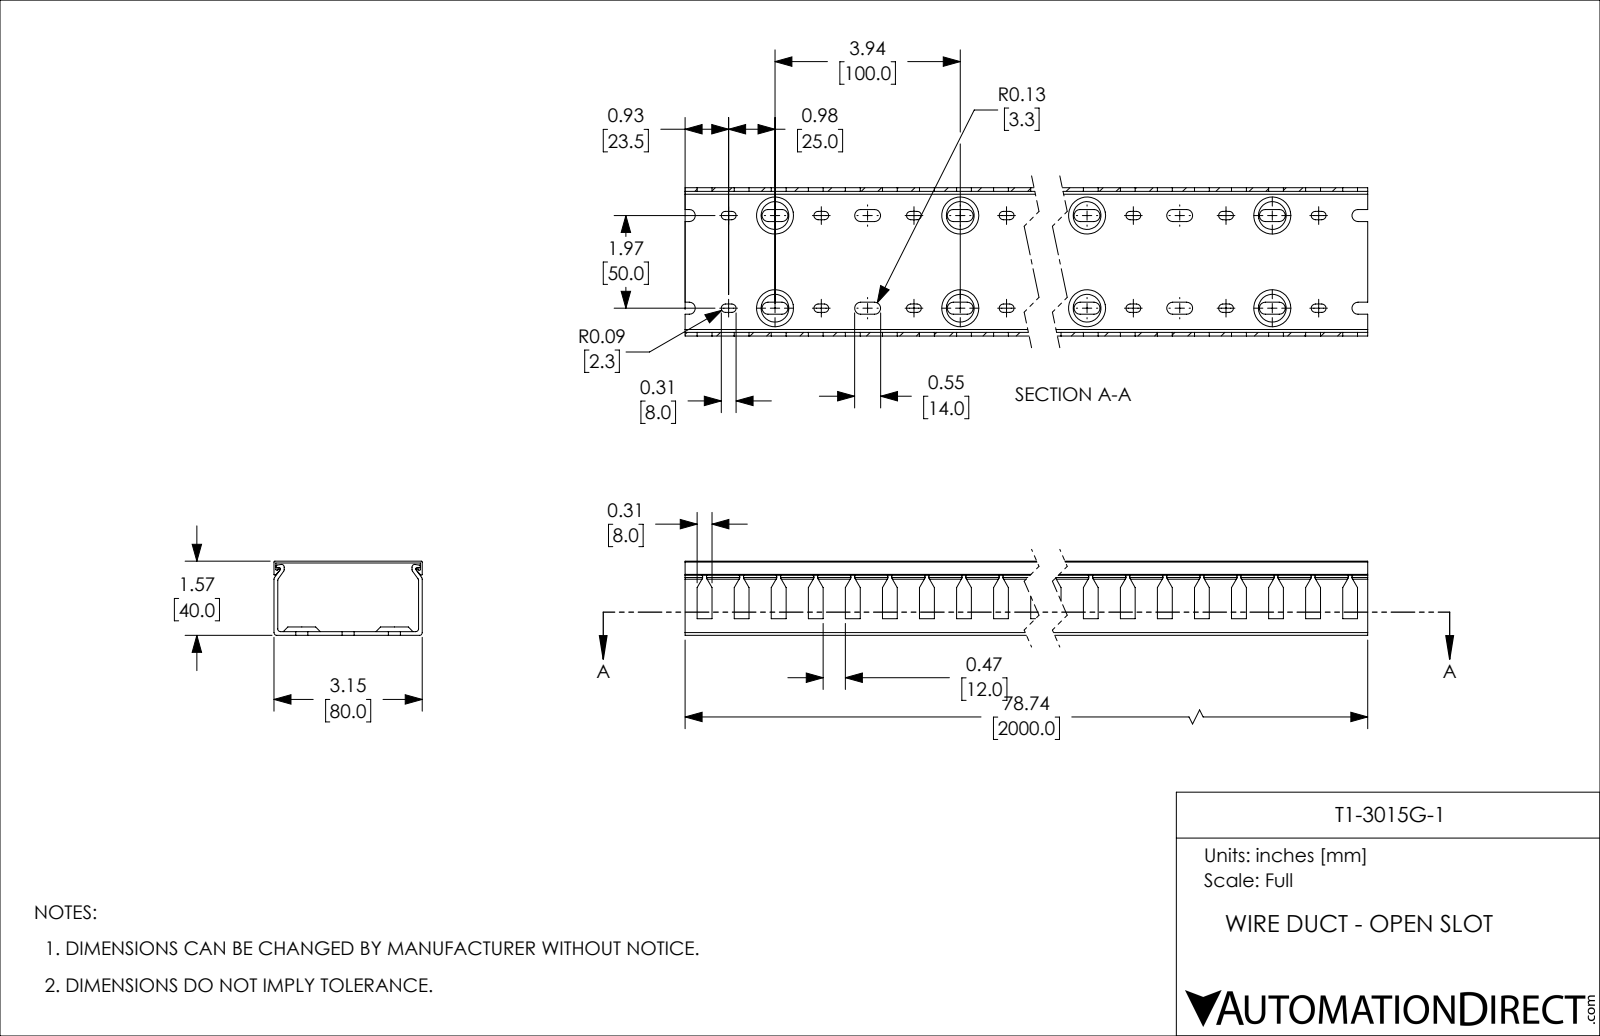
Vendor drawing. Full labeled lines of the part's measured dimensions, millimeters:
Part name (STEP PRODUCT): T1-3015G-1
STEP written by: SolidWorks 2021 (CONFIG_CONTROL_DESIGN)
Units: millimetres
Bodies: 2 solids, 1573 faces (762 planar, 731 cylindrical, 80 other)
Overall size (bounding box): 2000 × 80 × 40
Volume: 816 759 mm³ · Surface area: 1 013 000 mm²
Partial cylindrical surfaces — rounded edges, fillets, slot ends (radius × count): R3.25 ×200, R2.25 ×160, R1.5 ×12, R0.5 ×8, R0.75 ×6
Main face-to-face distances: 2, 1, 40, 39, 37, 38, 78, 80, 76, 79
